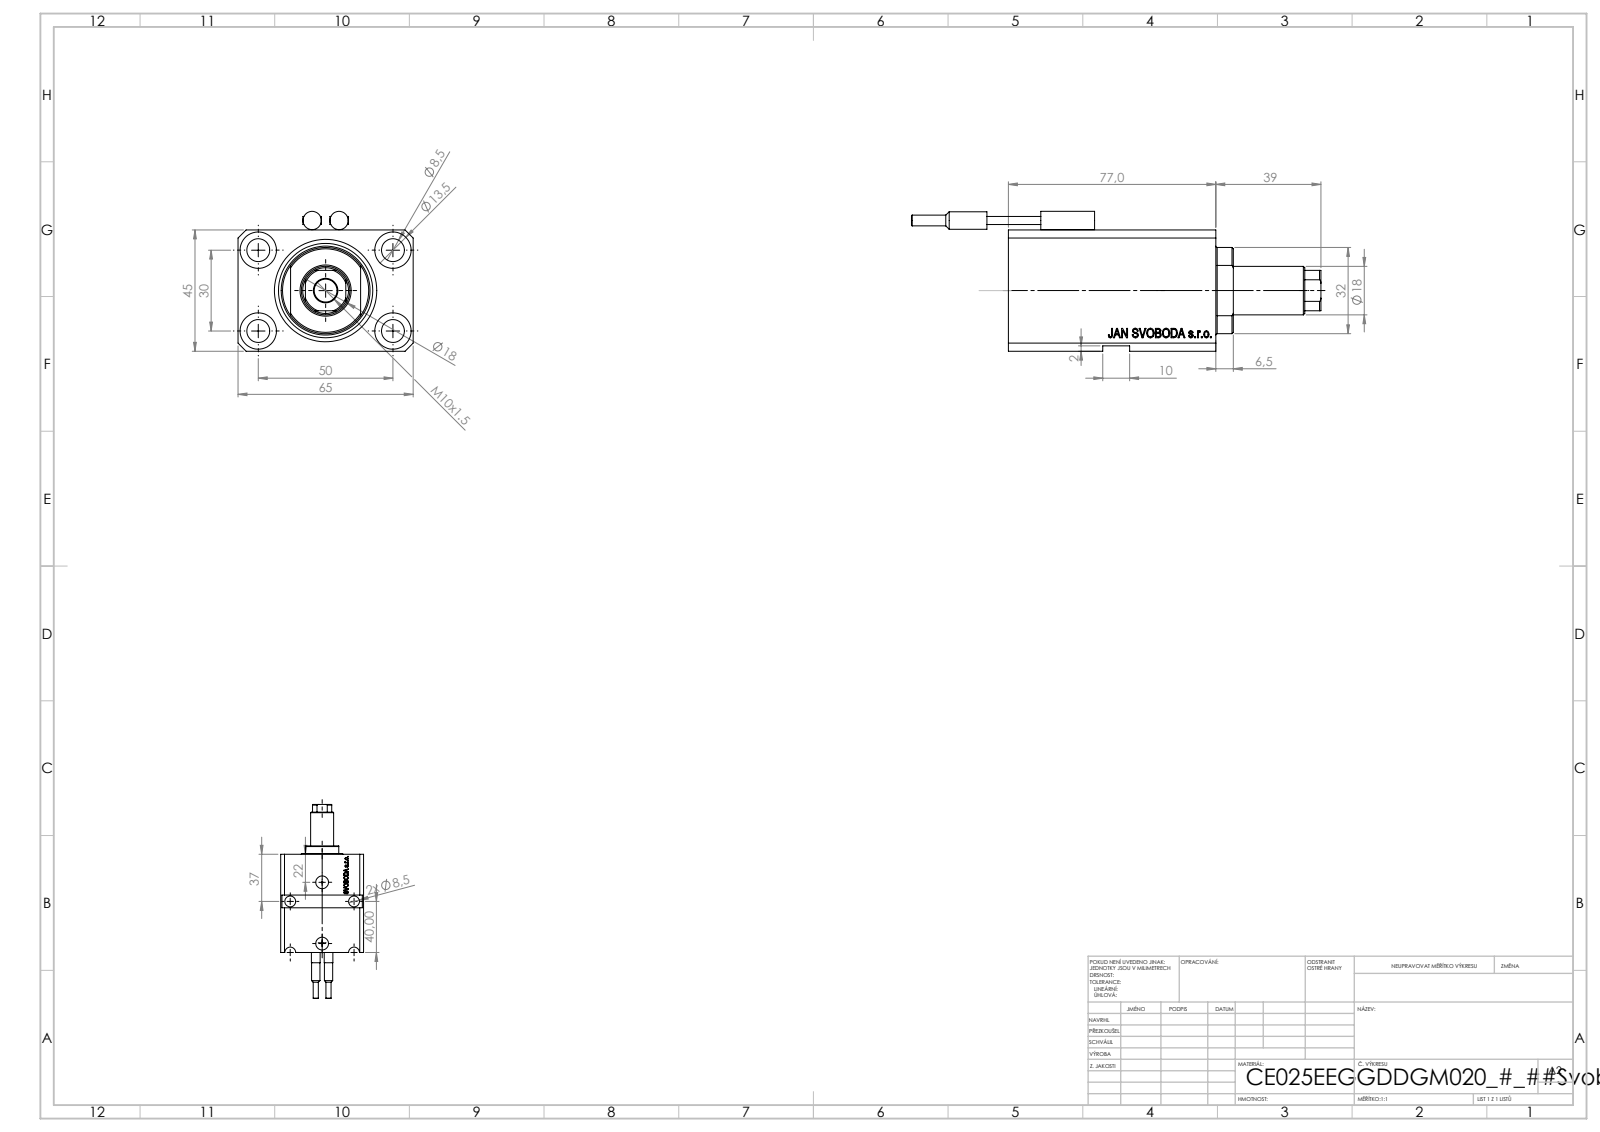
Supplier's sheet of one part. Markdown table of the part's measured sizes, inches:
| quantity | value |
| --- | --- |
| part name | V250CE_E_Body; SWITCH_V250CE; V250CE_C_VCP; V250CE_VC_E |
| STEP written by | SolidWorks 2019 (CONFIG_CONTROL_DESIGN) |
| units | inches |
| bodies | 5 solids, 942 faces (466 planar, 90 cylindrical, 386 other) |
| overall size | 5.984 × 2.559 × 2.043 |
| volume | 12.82 in³ |
| surface area | 83.55 in² |
| round holes (diameter × count) | 0.335 × 7, 0.531 × 4, 0.049 × 2, 0.394 × 2, 0.709 × 1, 0.984 × 1, 1.496 × 1 |
| round bosses / shafts (diameter × count) | 0.268 × 2, 0.256 × 2, 0.157 × 2 |
| partial cylindrical surfaces (radius × count) | 0.167 × 2, 0.335 × 1, 0.63 × 1 |
| main face-to-face distances | 1.772, 2.559, 2.043, 3.031, 0.988, 1.26, 0.783, 0.079, 2.677, 0.354 |
| hole center spacings | 1.148, 1.969, 1.181, 1.613, 1.63, 2.296, 0.021, 1.869 |
